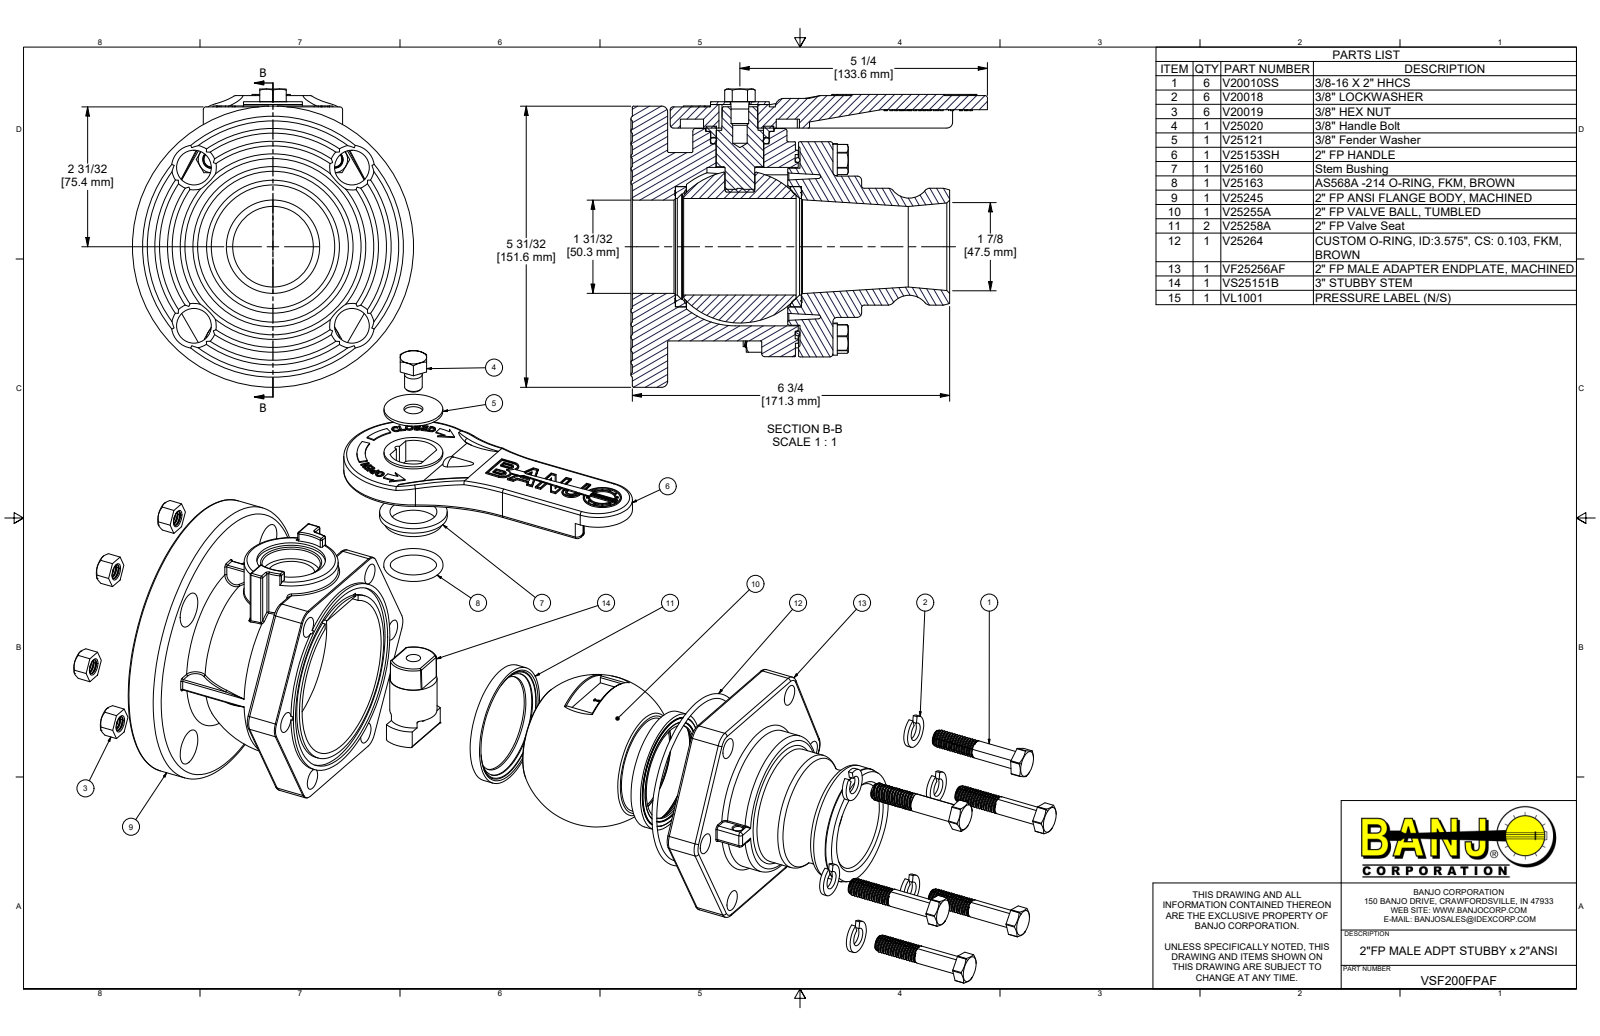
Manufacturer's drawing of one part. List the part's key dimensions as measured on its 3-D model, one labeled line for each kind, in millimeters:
Part name (STEP PRODUCT): VSF200FPAF; V25255A; V25255AM; V25255AX (+8 more)
STEP written by: Autodesk Inventor 2017 (AUTOMOTIVE_DESIGN)
Units: millimetres
Bodies: 31 solids, 5002 faces (2420 planar, 815 cylindrical, 1767 other)
Overall size (bounding box): 192.46 × 160.86 × 151.64
Volume: 1 100 000 mm³ · Surface area: 271 872 mm²
Round holes (diameter × count): ⌀11.18 ×8, ⌀7.81 ×6, ⌀9.78 ×6, ⌀19.05 ×4, ⌀5.33 ×2, ⌀9.52 ×2, ⌀7.8 ×1, ⌀10.31 ×1, ⌀13.83 ×1, ⌀19.55 ×1, ⌀25.4 ×1, ⌀25.81 ×1
Round bosses / shafts (diameter × count): ⌀8.24 ×90, ⌀9.52 ×7, ⌀17.46 ×6, ⌀151.64 ×1, ⌀104.14 ×1, ⌀101.6 ×1, ⌀91.06 ×1, ⌀84.71 ×1
Partial cylindrical surfaces — rounded edges, fillets, slot ends (radius × count): R1.52 ×42, R0.76 ×36, R4.12 ×12, R0.51 ×8, R0.81 ×6, R7.92 ×6, R7.94 ×6, R8.12 ×6
Main face-to-face distances: 19.05, 108.28, 89.23, 0.76, 17.78, 18.16, 1.53, 90.5, 71.45, 69.85
Hole centre spacings: 45.17, 45.2, 57.53, 60.32, 85.3, 108.88, 108.97, 10.45
